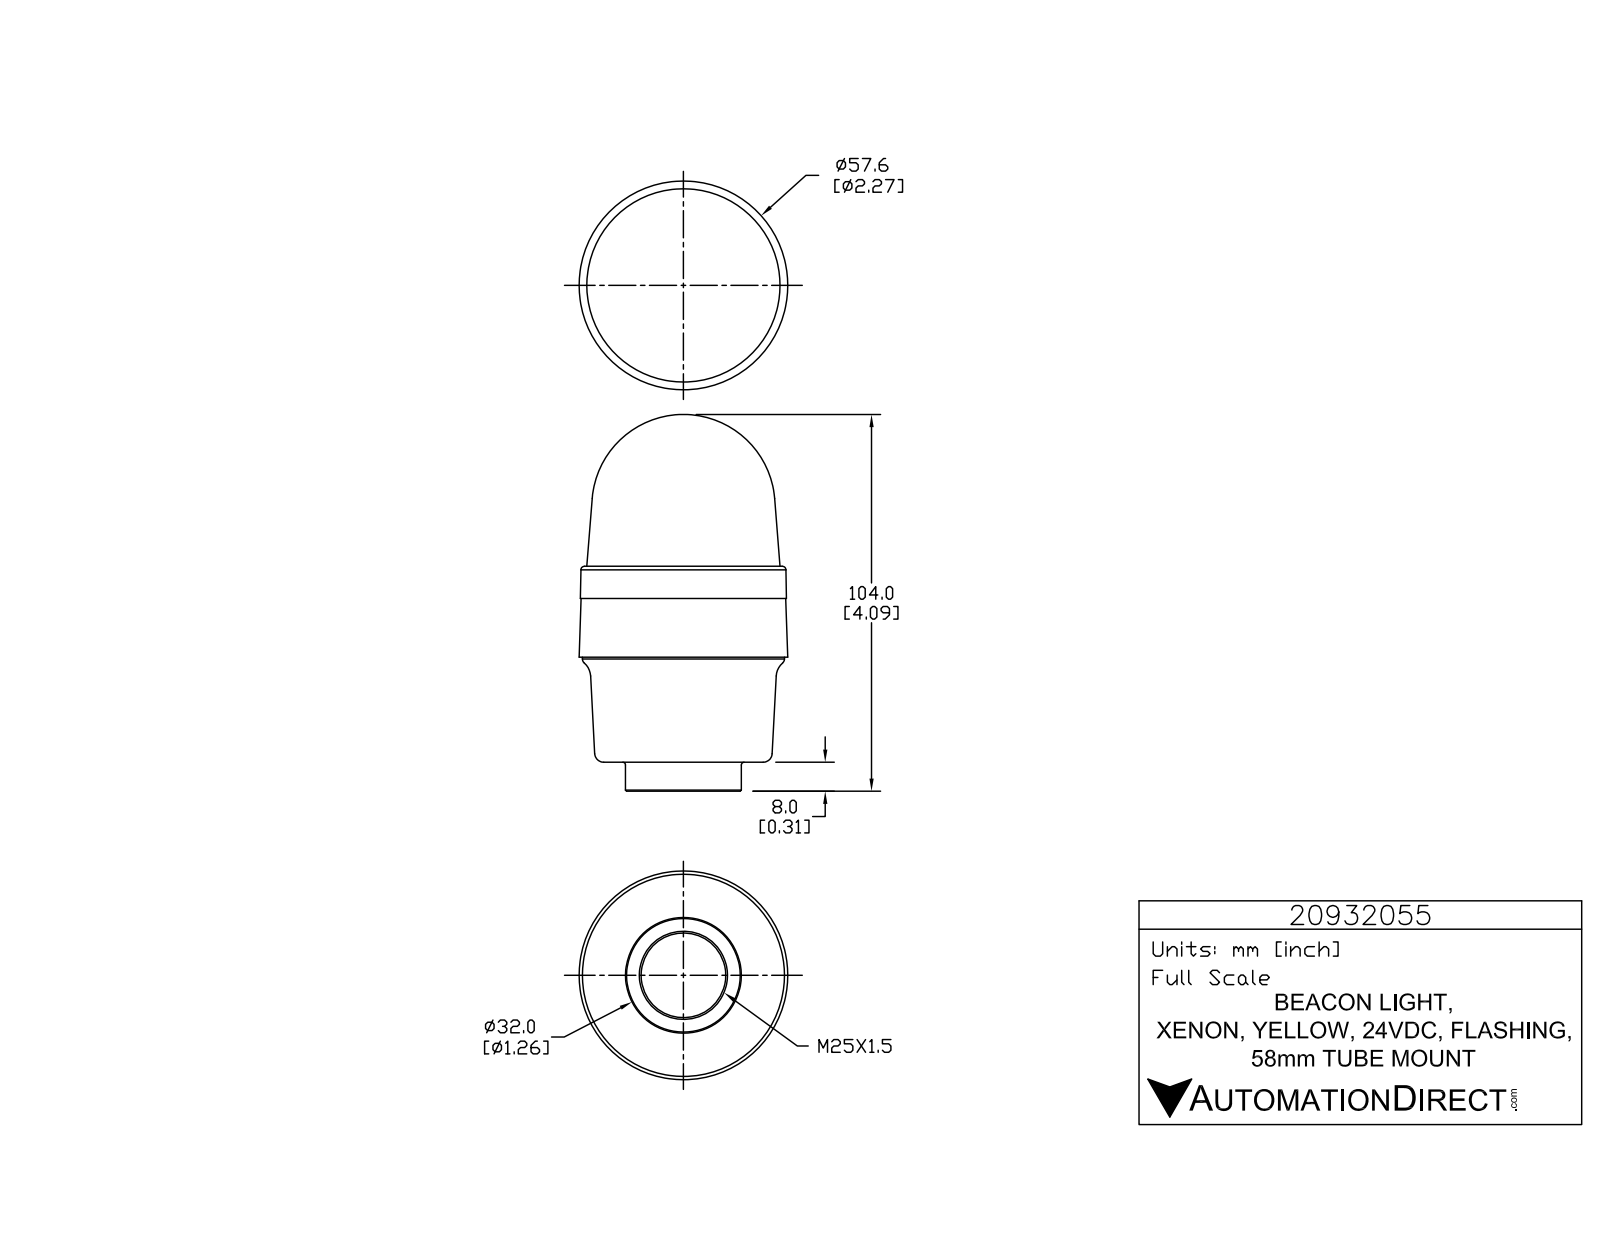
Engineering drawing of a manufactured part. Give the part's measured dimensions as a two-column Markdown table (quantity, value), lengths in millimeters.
| quantity | value |
| --- | --- |
| part name | 20932055 |
| STEP written by | SolidWorks 2015 (AUTOMOTIVE_DESIGN) |
| units | millimeters |
| bodies | 1 solid, 791 faces (525 planar, 168 cylindrical, 98 other) |
| overall size | 102.9 × 57.6 × 57.6 |
| volume | 192 100 mm³ |
| surface area | 19 310 mm² |
| round holes (diameter × count) | 1 × 3, 23.4 × 1 |
| round bosses / shafts (diameter × count) | 5.7 × 3, 1.4 × 3, 55.8 × 1, 32 × 1 |
| partial cylindrical surfaces (radius × count) | 0.2 × 6, 0.2 × 6, 0.2 × 6, 3.3 × 6, 0.1 × 3, 0.1 × 3, 0.2 × 3, 0.2 × 3 |
| main face-to-face distances | 8, 29, 37, 25.1, 54.1, 62.1, 8.9, 16.2, 45.2, 53.2 |
